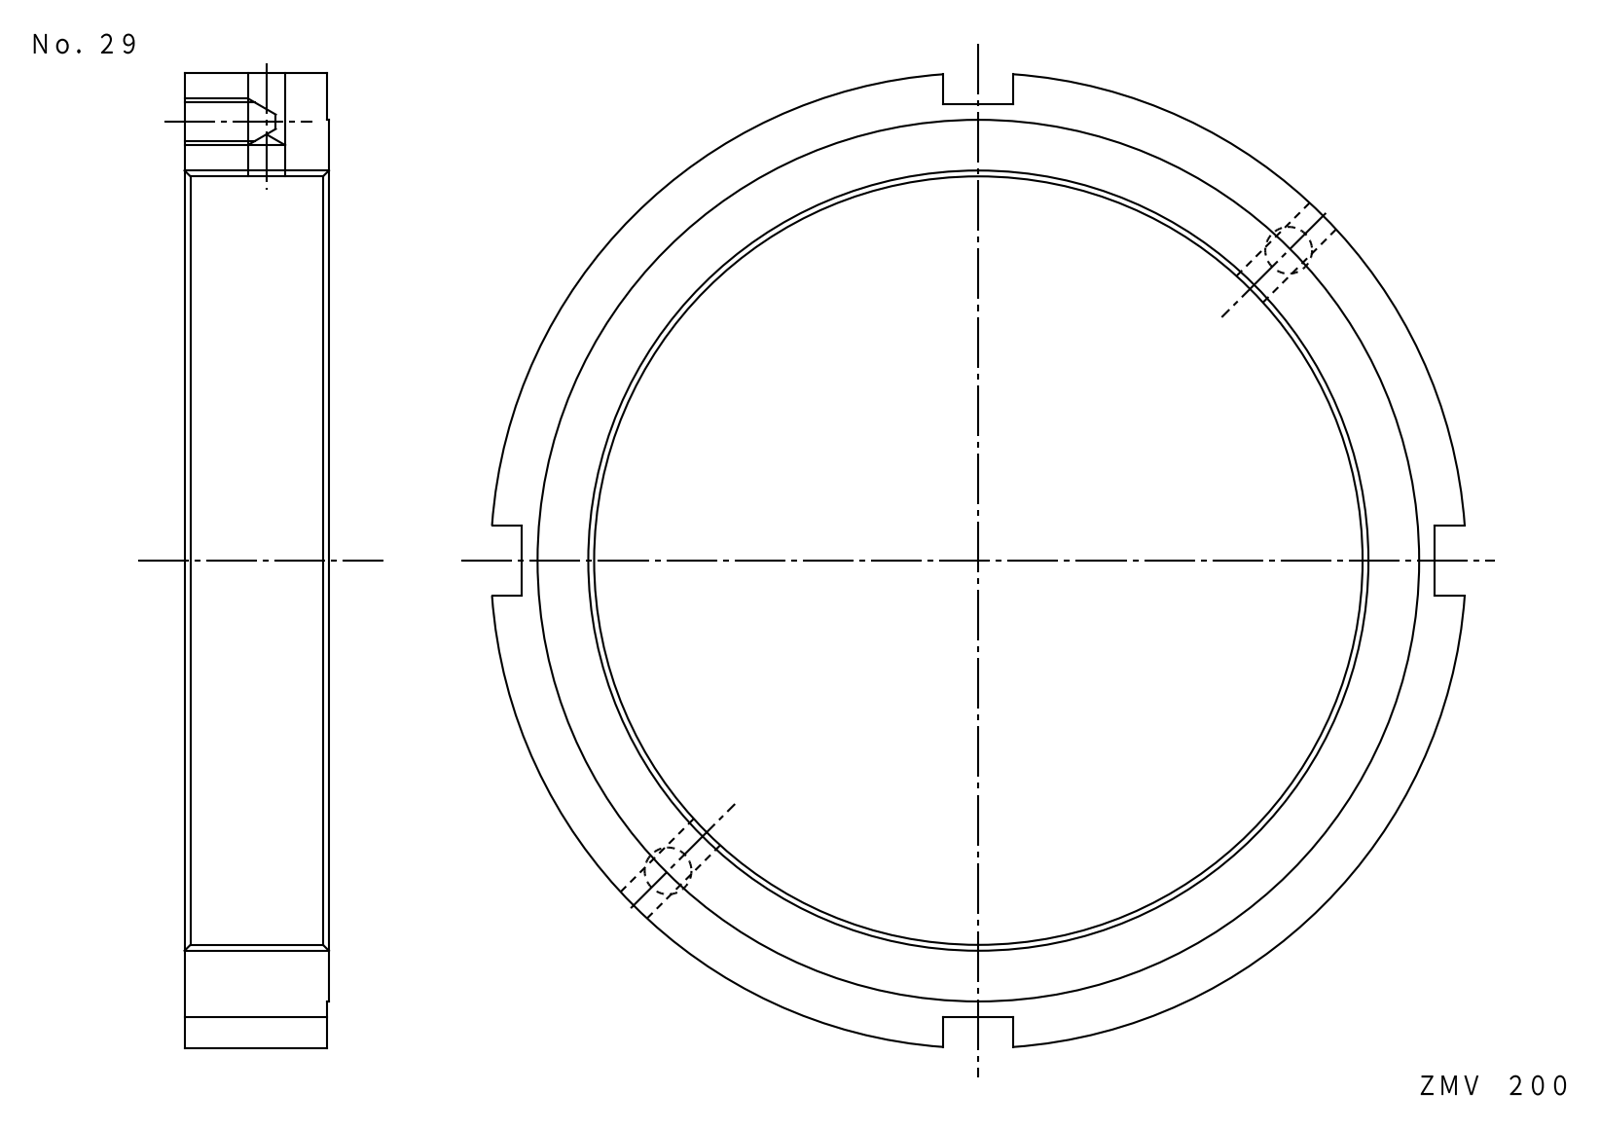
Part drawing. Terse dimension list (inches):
name: FKD ZMV200
written by: Autodesk Inventor LT (CONFIG_CONTROL_DESIGN)
unit: in
bodies: 1 solid, 29 faces (15 planar, 10 cylindrical, 4 other)
size: 9.817 × 9.817 × 1.457
volume: 37.97 in³; area: 140.6 in²
holes: 2× ⌀0.378, 2× ⌀0.398, 1× ⌀7.874
bosses: 1× ⌀9.843, 1× ⌀8.898
face distances: 1.457, 0.02, 1.437, 4.252, 4.961, 9.213, 0.709
hole spacings: 4.429, 8.858
